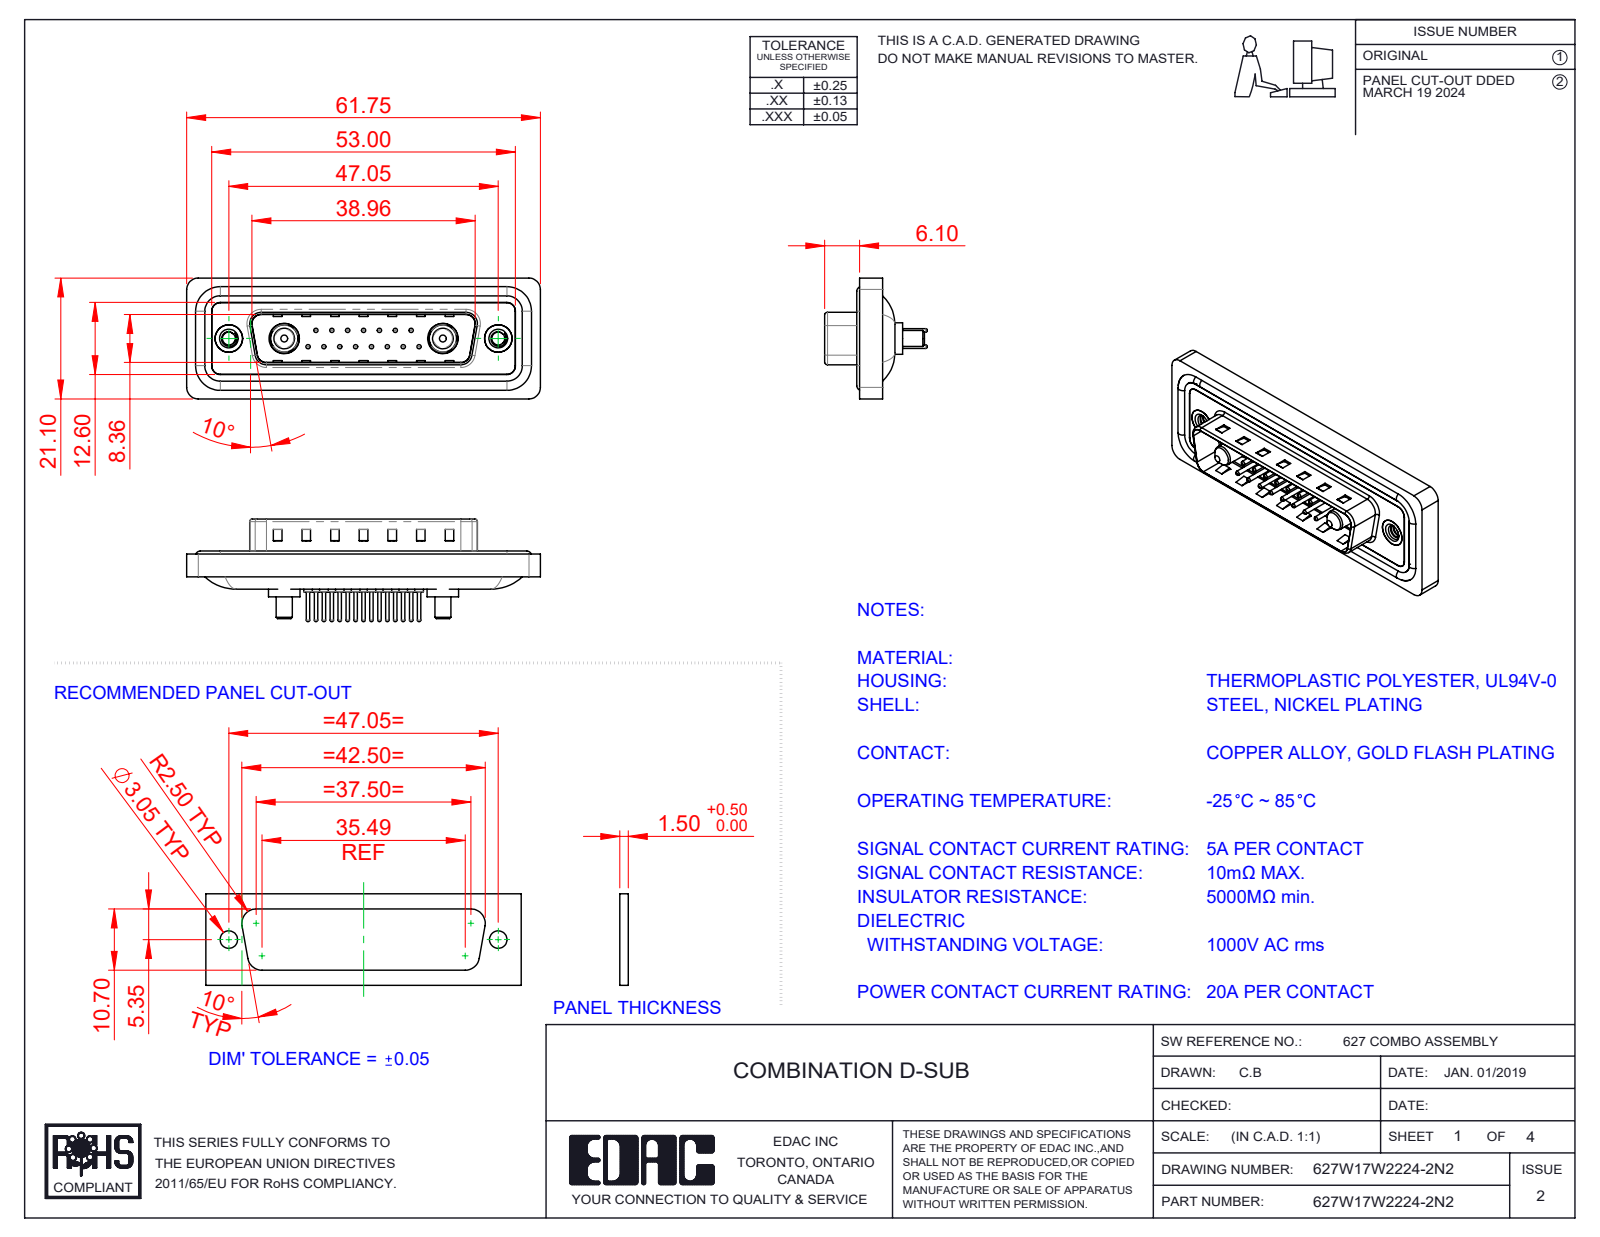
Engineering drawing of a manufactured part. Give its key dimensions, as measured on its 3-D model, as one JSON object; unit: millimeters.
{"part_name": "627W17W2224-2N2; 627Combo Contact Row 2_24; 627Combo Shell Rear_25 Contacts; 627Combo Threaded Rivet_2 (+5 more)", "step_written_by": "SolidWorks 2023 (CONFIG_CONTROL_DESIGN)", "units": "millimeters", "bodies": {"solids": 26, "faces": 1116, "planar": 334, "cylindrical": 436, "other": 346}, "overall_size": [61.75, 21.1, 17.9], "volume_mm3": 7266, "surface_area_mm2": 11914, "round_holes": [[0.75, 15], [1.6, 15], [2, 15], [2.26, 2], [4, 2], [4.8, 2], [4.85, 2], [5, 2], [5.3, 2]], "round_bosses_or_shafts": [[1.5, 15], [0.6, 15], [1.6, 4], [5.5, 2], [5.2, 2], [4.9, 2], [4.75, 2], [3.75, 2]], "partial_cylinders_radius": [[1.5, 22], [2, 18], [0.5, 8], [1.6, 8], [0.25, 4], [0.6, 4], [0.65, 4], [0.9, 4]], "face_to_face_distances": [0.4, 1.5, 1.1, 1.6, 0.5, 3.1, 2.9, 0.82, 9.58, 4.1], "hole_center_spacings": [3.16, 2.77, 5.54, 8.31, 5.04, 7.49, 11.08, 5.03]}
